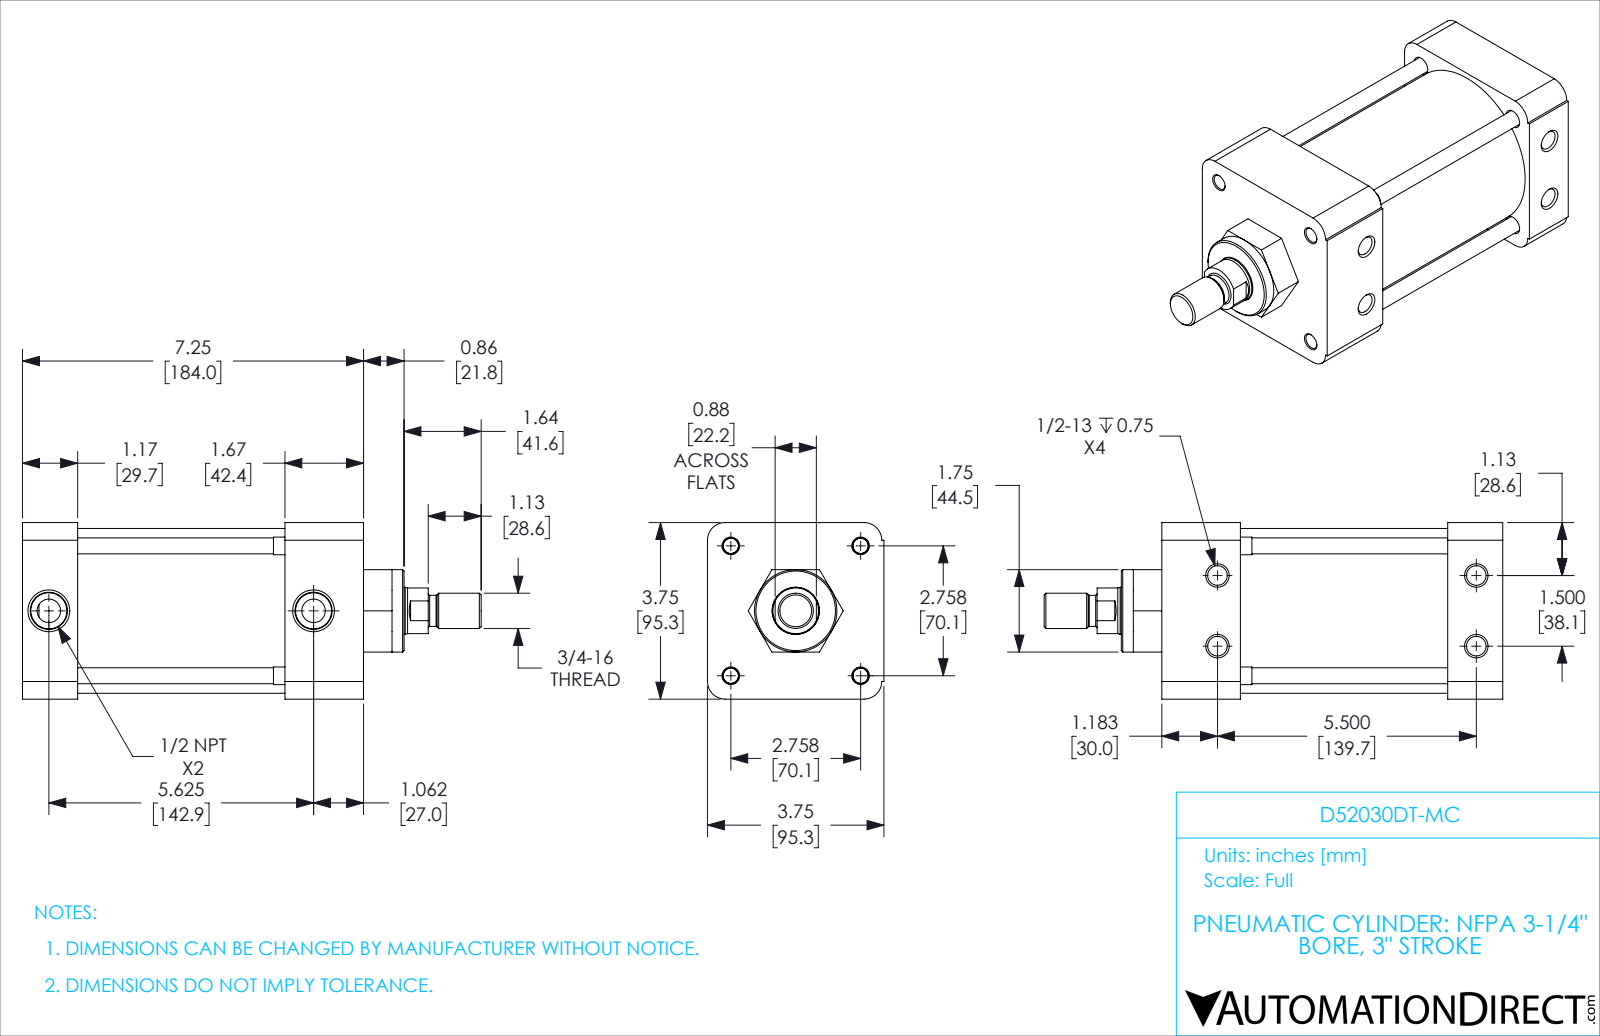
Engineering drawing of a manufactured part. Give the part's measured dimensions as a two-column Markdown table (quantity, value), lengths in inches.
| quantity | value |
| --- | --- |
| part name | D52030DT-M BODY; D52030DT-MC; D52030DT-M PISTON |
| STEP written by | SolidWorks 2015 (AUTOMOTIVE_DESIGN) |
| units | inches |
| bodies | 12 solids, 303 faces (99 planar, 114 cylindrical, 90 other) |
| overall size | 9.745 × 3.75 × 3.75 |
| volume | 61.24 in³ |
| surface area | 322.9 in² |
| round holes (diameter × count) | 0.33 × 4, 0.406 × 4, 0.417 × 4, 0.625 × 4, 0.5 × 2, 0.766 × 2, 1 × 1, 1.003 × 1, 3.25 × 1 |
| round bosses / shafts (diameter × count) | 0.609 × 4, 0.375 × 4, 0.34 × 4, 3.5 × 1, 3.247 × 1, 1.75 × 1, 0.997 × 1, 0.97 × 1 |
| partial cylindrical surfaces (radius × count) | 0.375 × 4 |
| main face-to-face distances | 3.75, 0.08, 4.326, 7.246, 1.75, 5.997, 1.249, 4.751, 1.246, 2.495 |
| hole center spacings | 1.95, 2.758, 0.75, 0.76, 1.5, 3.901, 5.5, 5.555 |
